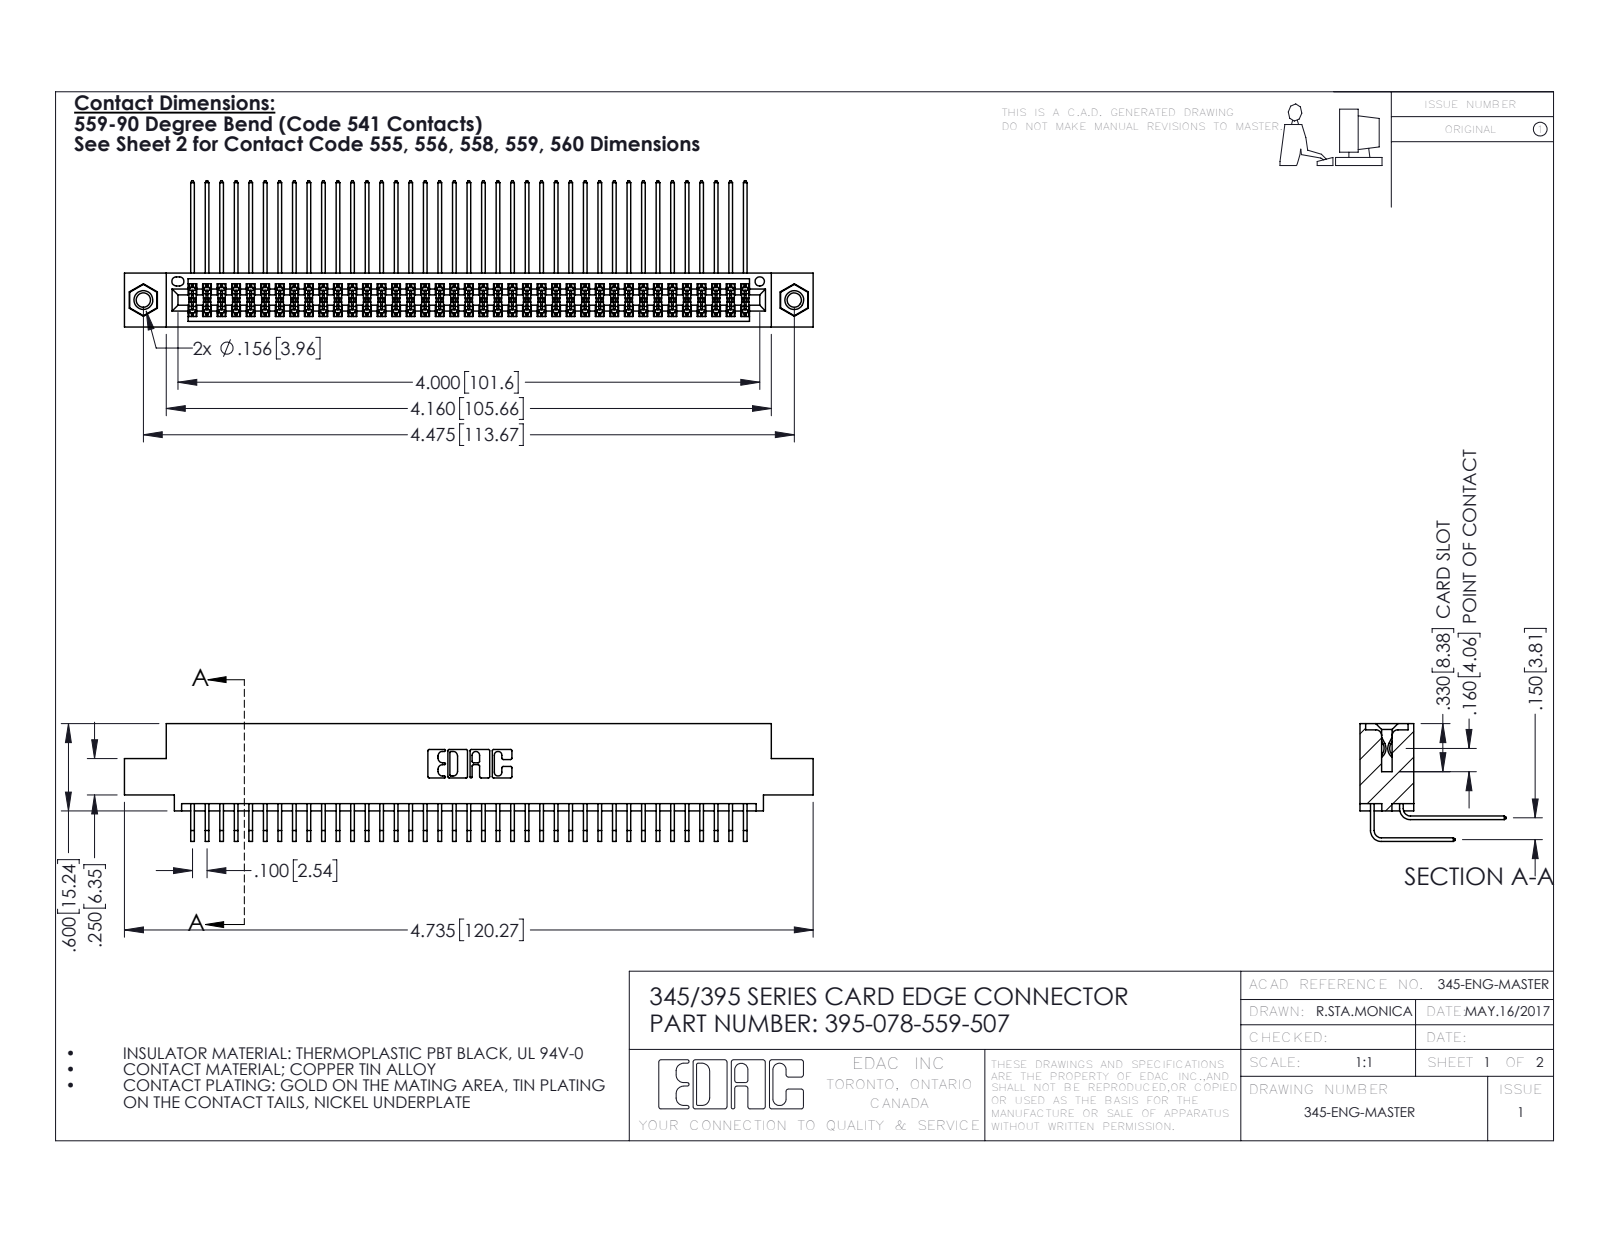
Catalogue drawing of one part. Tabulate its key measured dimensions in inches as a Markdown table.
| quantity | value |
| --- | --- |
| part name | 345-292-001_559 Tail - 2; 345-250-001_345-250-005-103; 395-078-559-507; 345-292-001_558 559 Tail - 1 (+1 more) |
| STEP written by | SolidWorks 2016 (CONFIG_CONTROL_DESIGN) |
| units | inches |
| bodies | 81 solids, 4246 faces (2846 planar, 1384 cylindrical, 16 other) |
| overall size | 4.735 × 1.005 × 0.809 |
| volume | 0.733 in³ |
| surface area | 30.91 in² |
| round holes (diameter × count) | 0.098 × 2, 0.125 × 2, 0.156 × 2, 0.064 × 1 |
| round bosses / shafts (diameter × count) | 0.155 × 2 |
| partial cylindrical surfaces (radius × count) | 0.006 × 117, 0.01 × 22, 0.007 × 6, 0.031 × 6, 0.026 × 3, 0.014 × 2, 0.019 × 2, 0.022 × 2 |
| main face-to-face distances | 0.072, 0.298, 0.2, 0.37, 0.098, 0.272, 0.025, 0.225, 0.175, 0.15 |
| hole center spacings | 0.27, 4.239, 4.475 |
